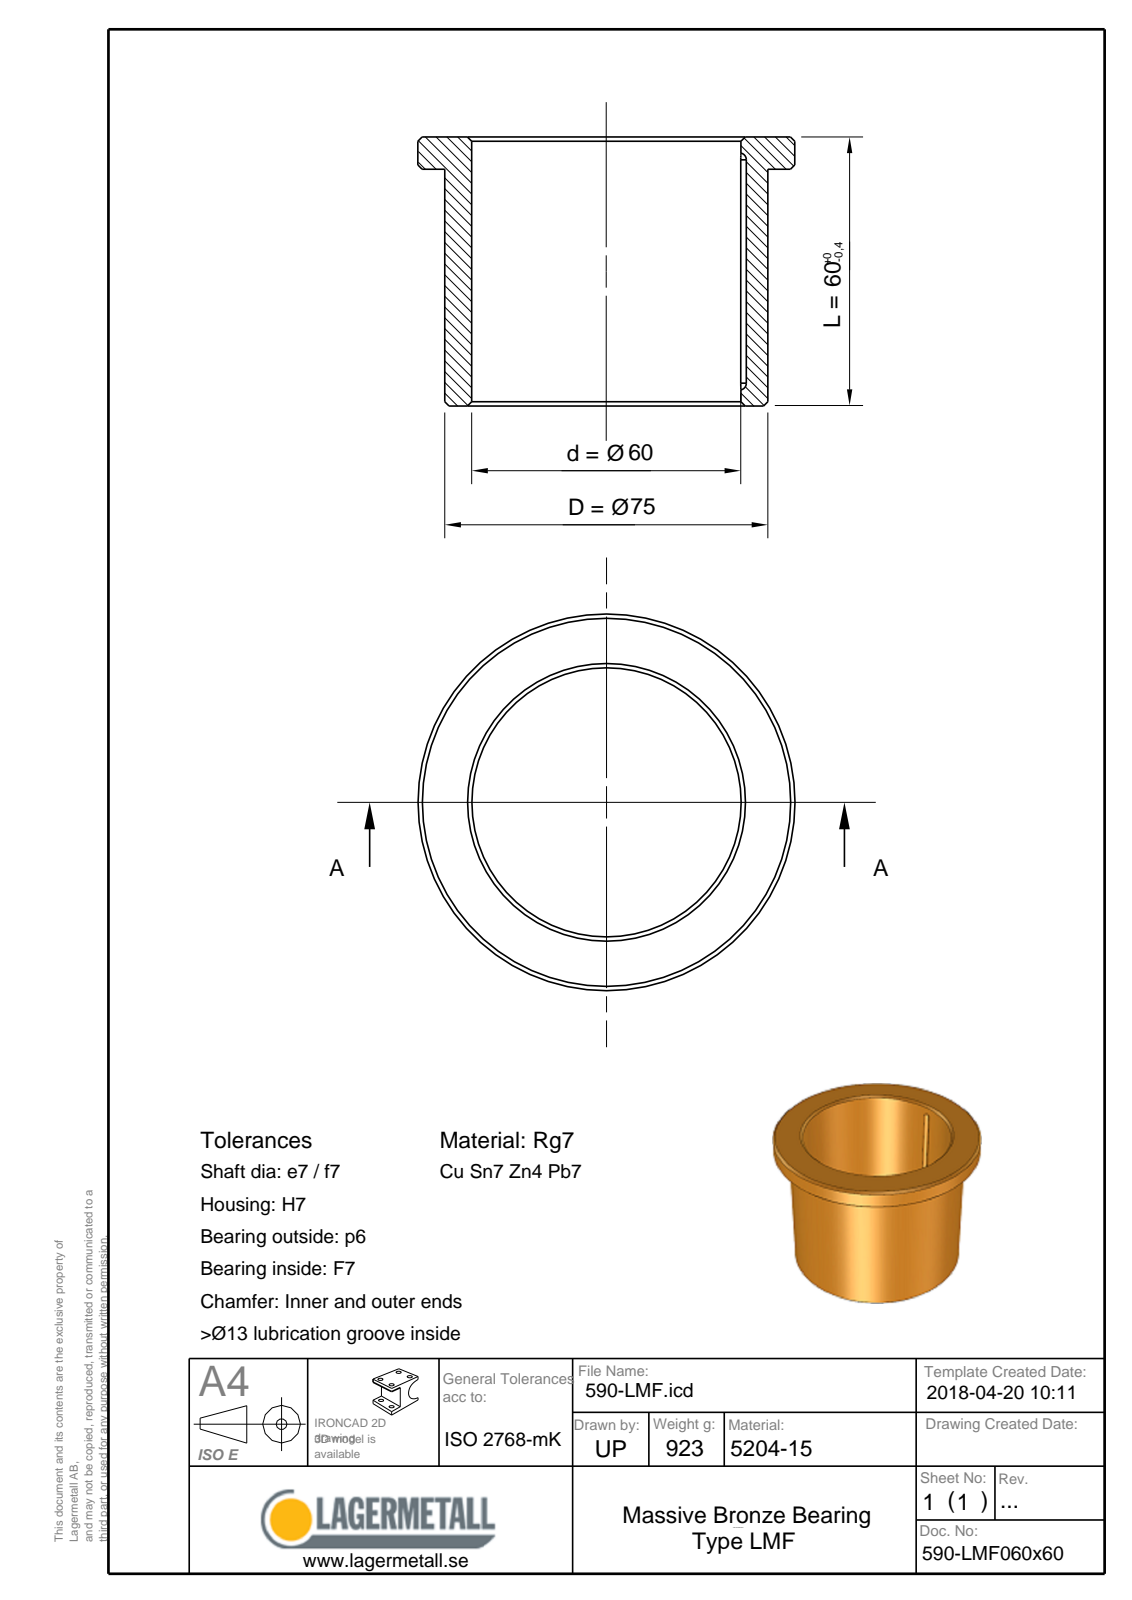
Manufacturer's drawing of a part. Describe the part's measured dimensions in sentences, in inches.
The part is named "590-LMF060x60". Its 3-D file was written by "Spatial InterOp 3D (CONFIG_CONTROL_DESIGN)". It is 1 solid with 16 faces: 4 planar, 5 cylindrical and 7 other. Overall it measures 3.346 by 3.346 by 2.362 inches. Its volume is 6.402 cubic inches and its surface area 47.96 square inches. Round holes: 1 of diameter 2.362. Round bosses or shafts: 1 of diameter 3.346, 1 of diameter 2.953. Partial cylindrical surfaces (rounded edges, fillets, slot ends): 2 of radius 0.069. The main face-to-face distances are 2.362, 2.047, 0.315.
